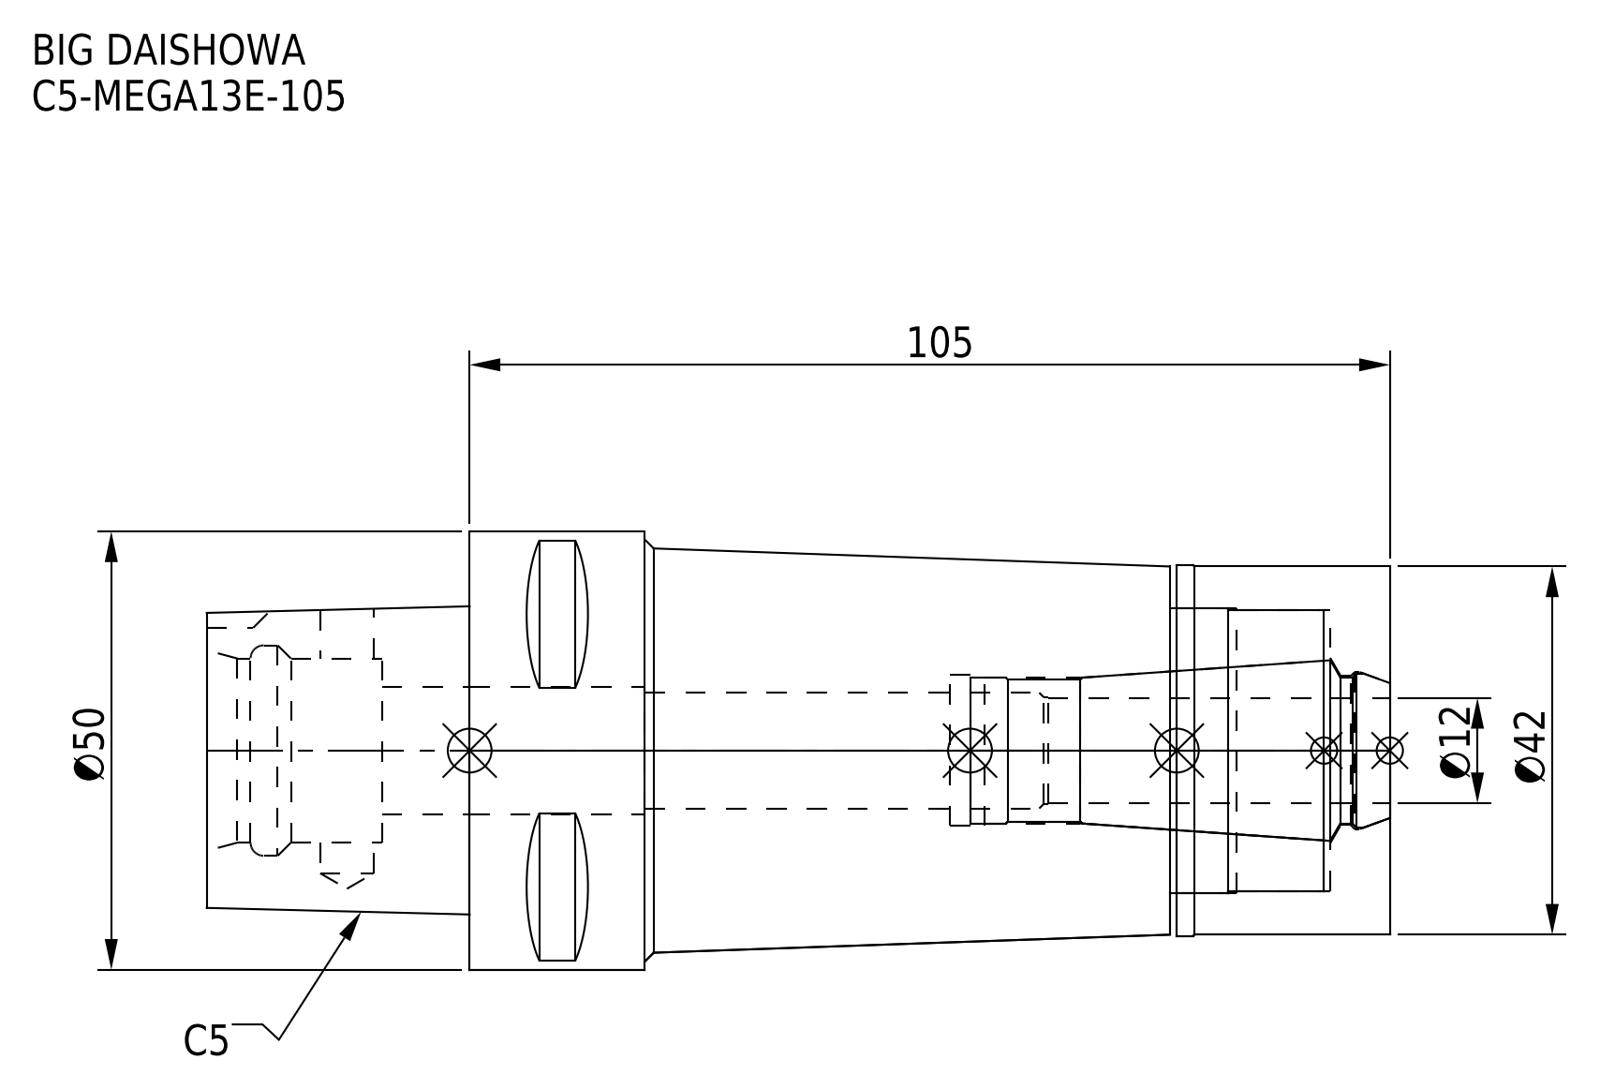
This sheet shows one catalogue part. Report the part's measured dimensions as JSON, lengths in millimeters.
{"part_name": "C5-MEGA13E-105_1.stp; C5-MEGA13E-105-120.stp; C5-MEGA13E-105; MEN13_1.stp (+3 more)", "step_written_by": "SolidWorks 2019 (CONFIG_CONTROL_DESIGN)", "units": "millimeters", "bodies": {"solids": 2, "faces": 97, "planar": 36, "cylindrical": 37, "other": 24}, "overall_size": [135, 50, 50], "volume_mm3": 161278, "surface_area_mm2": 34256, "round_holes": [[6.1, 1], [13.3, 1], [14.5, 1], [16.6, 1], [17, 1], [17.2, 1], [17.9, 1], [21, 1], [24, 1], [32, 1], [32.5, 1]], "round_bosses_or_shafts": [[50, 1], [42.3, 1], [42, 1]], "partial_cylinders_radius": [[4, 1]], "face_to_face_distances": [105, 25.1, 24.3, 80.7, 0.8, 79.9, 30, 97.5, 6.8, 17.5]}
